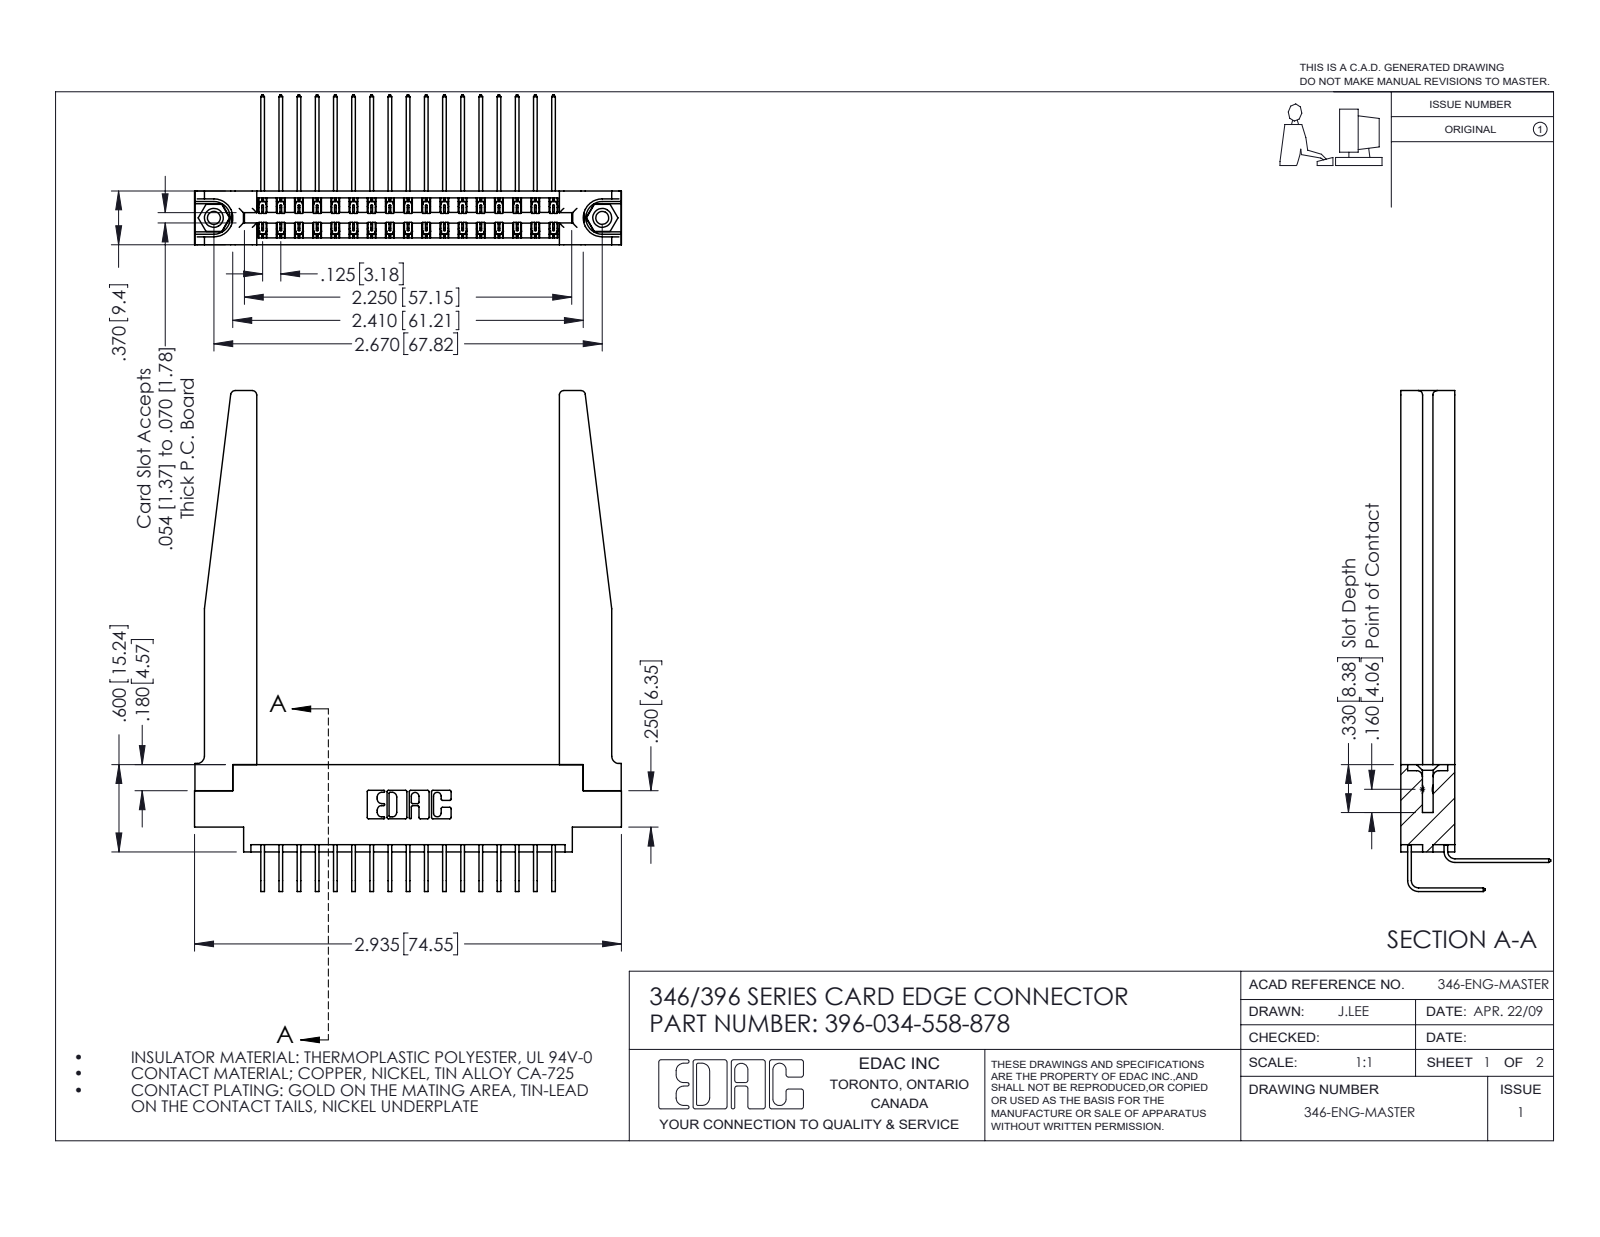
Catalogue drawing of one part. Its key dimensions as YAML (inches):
part_name: "346-220-078_345-220-078; 345-292-001_558 Tail - 2; 345-292-001_558 559 Tail - 1; 345-250-001_345-250-001-102 (+2 more)"
step_written_by: "SolidWorks 2016 (CONFIG_CONTROL_DESIGN)"
units: inches
bodies: {solids: 39, faces: 2196, planar: 1480, cylindrical: 664, other: 52}
overall_size: [3.443, 2.935, 1.03]
volume: 0.856
surface_area: 26.42
round_holes:
  - {diameter: 0.089, count: 2}
  - {diameter: 0.125, count: 2}
  - {diameter: 0.156, count: 2}
  - {diameter: 0.064, count: 1}
round_bosses_or_shafts:
  - {diameter: 0.155, count: 2}
partial_cylinders:
  - {radius: 0.006, count: 51}
  - {radius: 0.01, count: 22}
  - {radius: 0.03, count: 8}
  - {radius: 0.007, count: 6}
  - {radius: 0.031, count: 6}
  - {radius: 0.05, count: 4}
  - {radius: 0.026, count: 3}
  - {radius: 0.014, count: 2}
face_to_face_distances: [0.37, 0.322, 0.048, 0.072, 0.15, 0.148, 0.025, 0.25, 0.298, 0.22]
hole_center_spacings: [0.246, 2.463, 2.67]
